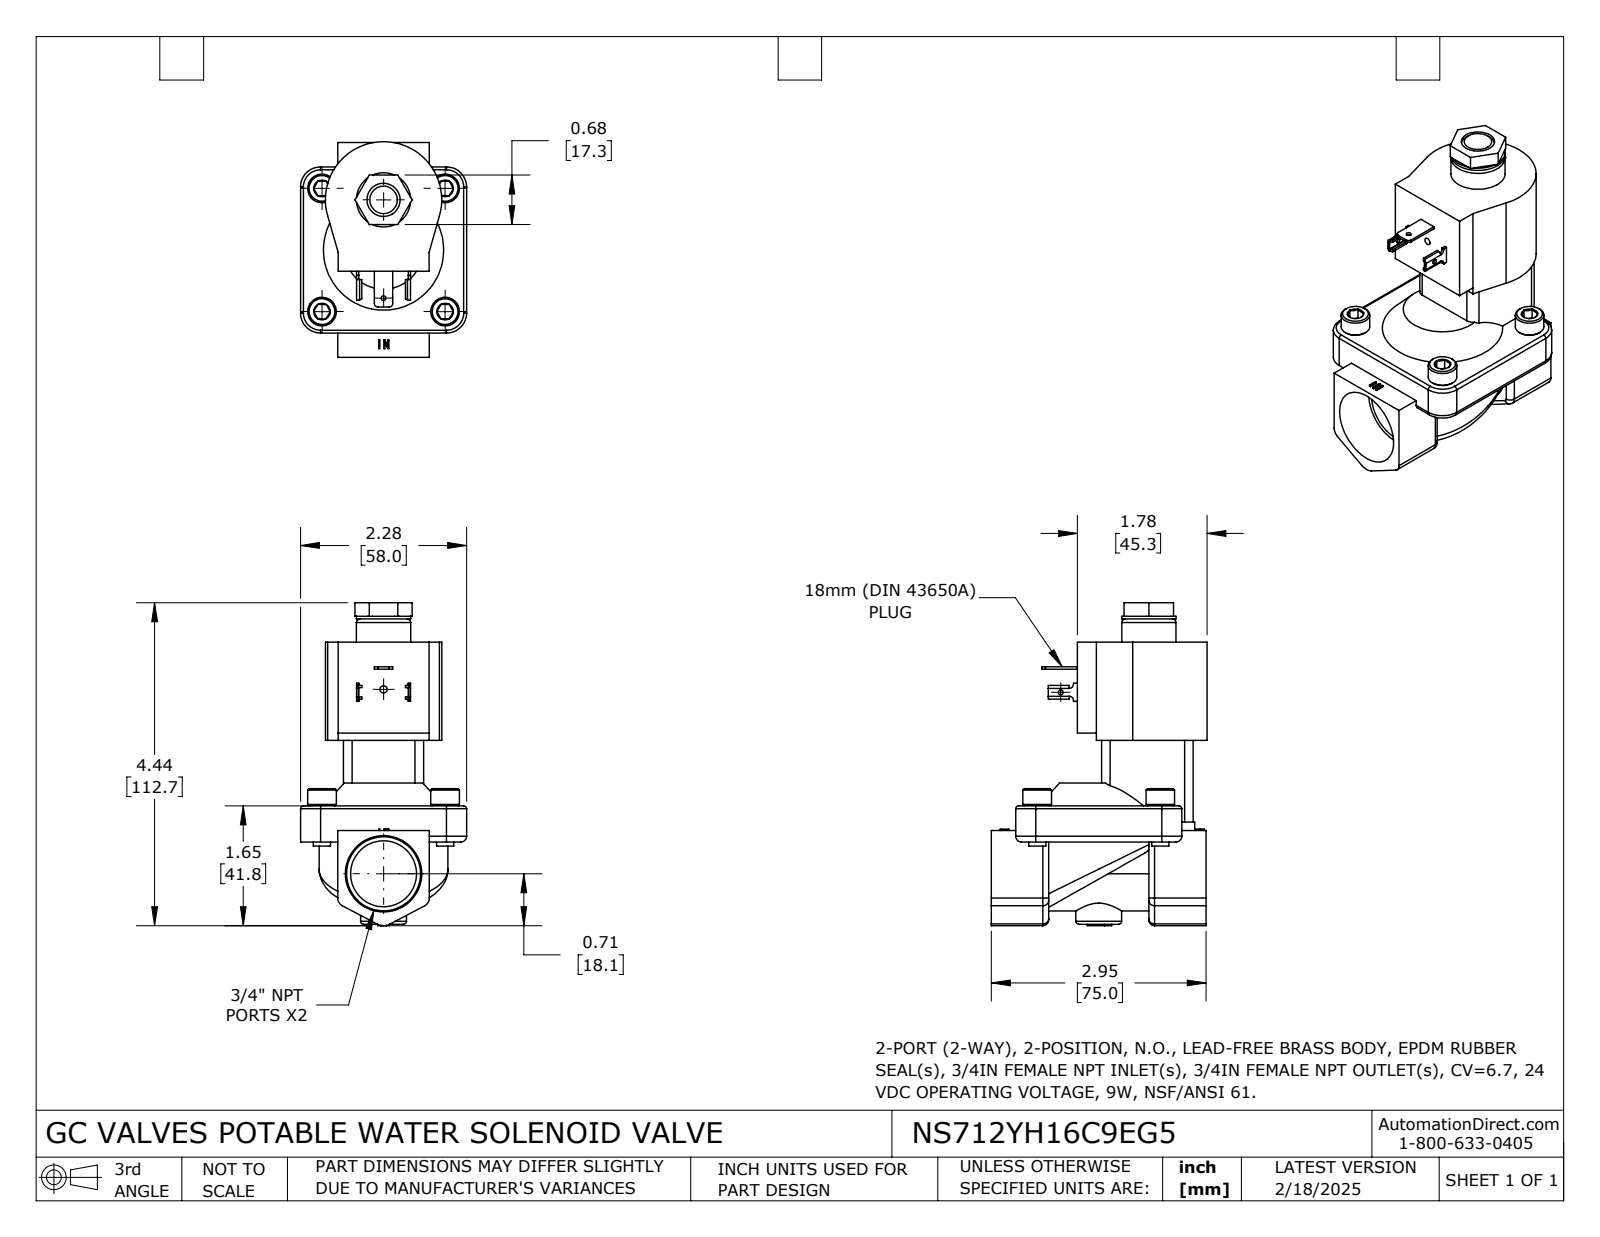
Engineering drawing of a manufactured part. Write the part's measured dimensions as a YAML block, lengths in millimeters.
part_name: "NS712YH16C9EG5"
step_written_by: "SolidWorks 2024 (CONFIG_CONTROL_DESIGN)"
units: millimeters
bodies: {solids: 1, faces: 379, planar: 195, cylindrical: 95, other: 89}
overall_size: [112.71, 75.32, 58]
volume: 161462
surface_area: 32099
round_holes:
  - {diameter: 1.68, count: 1}
  - {diameter: 1.7, count: 1}
  - {diameter: 2.53, count: 1}
  - {diameter: 11.58, count: 1}
  - {diameter: 23.01, count: 1}
  - {diameter: 30.48, count: 1}
round_bosses_or_shafts:
  - {diameter: 10, count: 4}
  - {diameter: 6, count: 4}
  - {diameter: 18.95, count: 1}
  - {diameter: 16, count: 1}
partial_cylinders:
  - {radius: 2, count: 11}
  - {radius: 3, count: 6}
  - {radius: 0.15, count: 4}
  - {radius: 1, count: 4}
  - {radius: 1.04, count: 4}
  - {radius: 7, count: 4}
  - {radius: 1.27, count: 2}
  - {radius: 1.52, count: 2}
face_to_face_distances: [30, 2, 57.19, 32, 43, 15, 13, 45, 12.6, 69.79]
hole_center_spacings: [34.29, 64.36]
